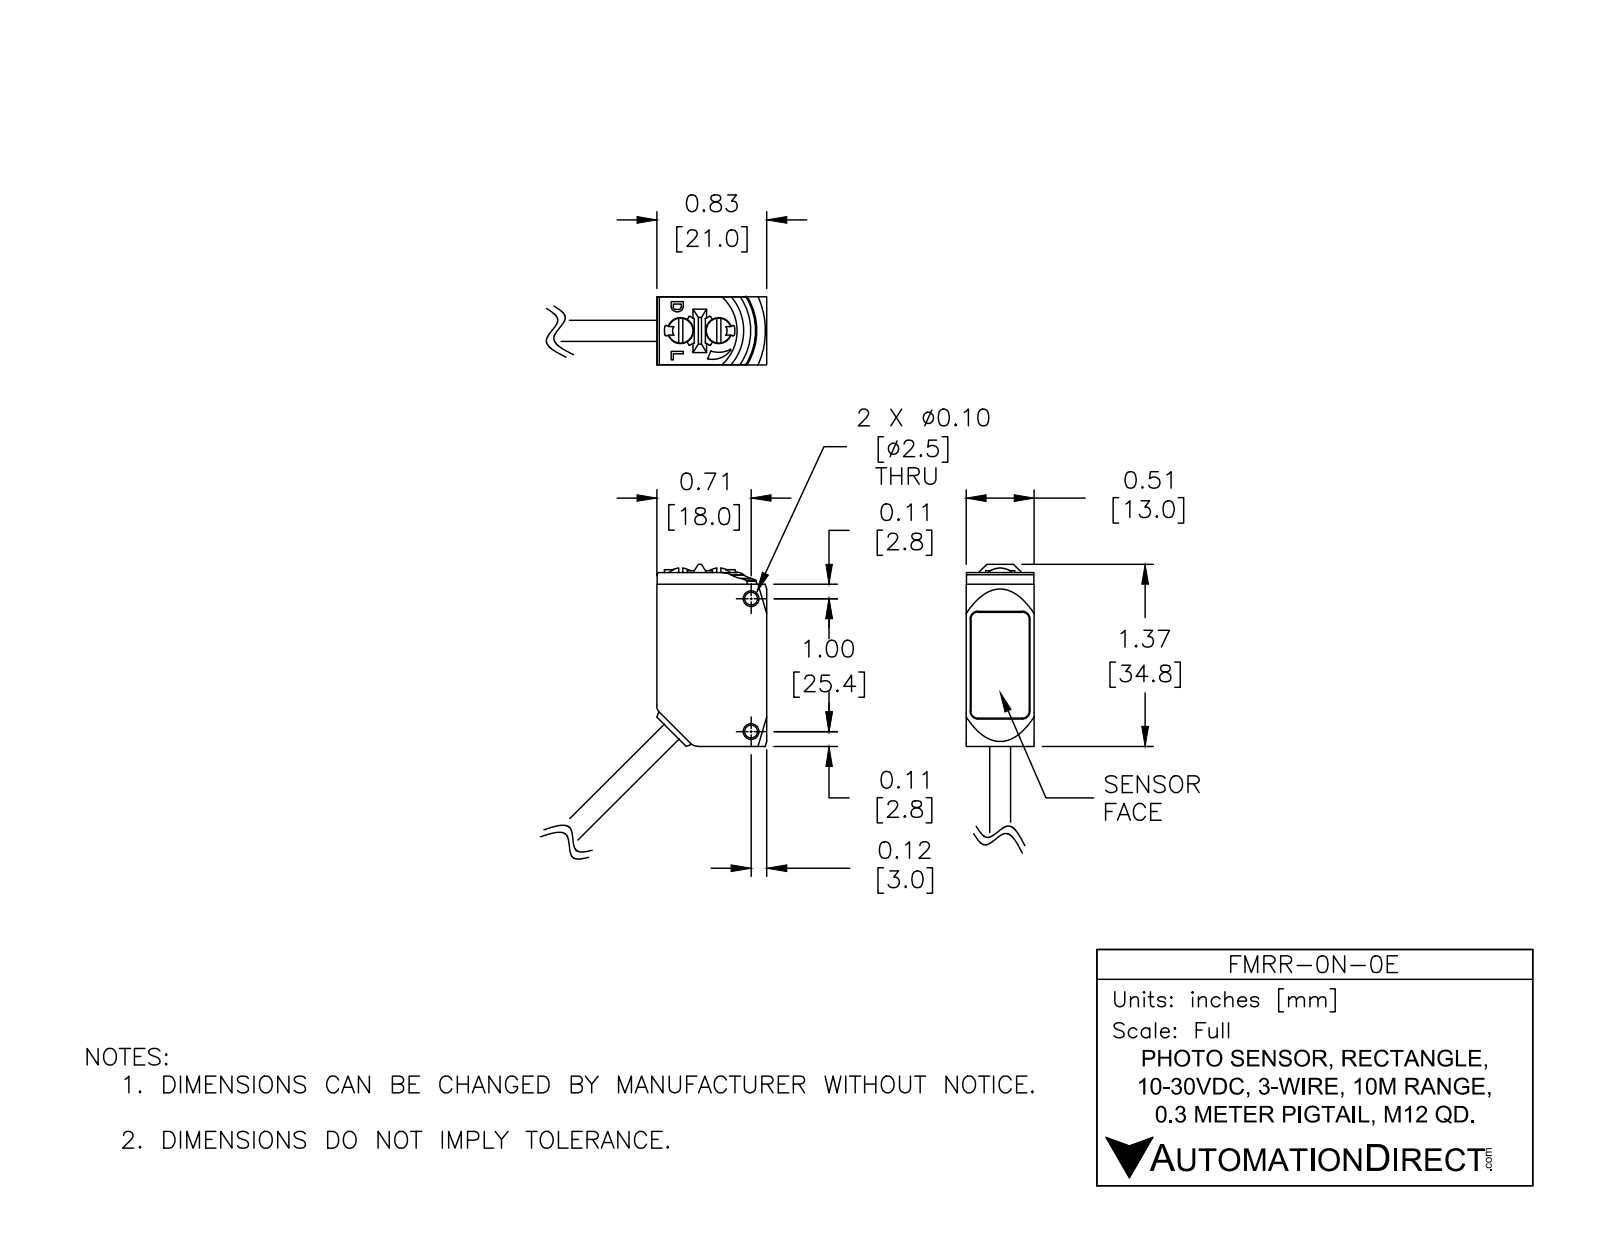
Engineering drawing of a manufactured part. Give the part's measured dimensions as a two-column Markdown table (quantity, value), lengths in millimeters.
| quantity | value |
| --- | --- |
| part name | FMRR-0N-0E |
| STEP written by | SolidWorks 2017 (AUTOMOTIVE_DESIGN) |
| units | millimeters |
| bodies | 1 solid, 186 faces (89 planar, 72 cylindrical, 25 other) |
| overall size | 52.9 × 39.1 × 13 |
| volume | 8 880 mm³ |
| surface area | 3 533 mm² |
| round holes (diameter × count) | 2.5 × 2, 5 × 2 |
| round bosses / shafts (diameter × count) | 4.8 × 2, 4 × 1 |
| partial cylindrical surfaces (radius × count) | 0.5 × 7, 0.5 × 7, 0.2 × 4, 0.3 × 4, 1.3 × 4, 1.5 × 4, 0.1 × 3, 0.5 × 2 |
| main face-to-face distances | 13, 21, 33.2, 0.9, 13, 0.8, 12.2, 0.9, 12, 12 |
| hole center spacings | 7.3, 25.4 |
